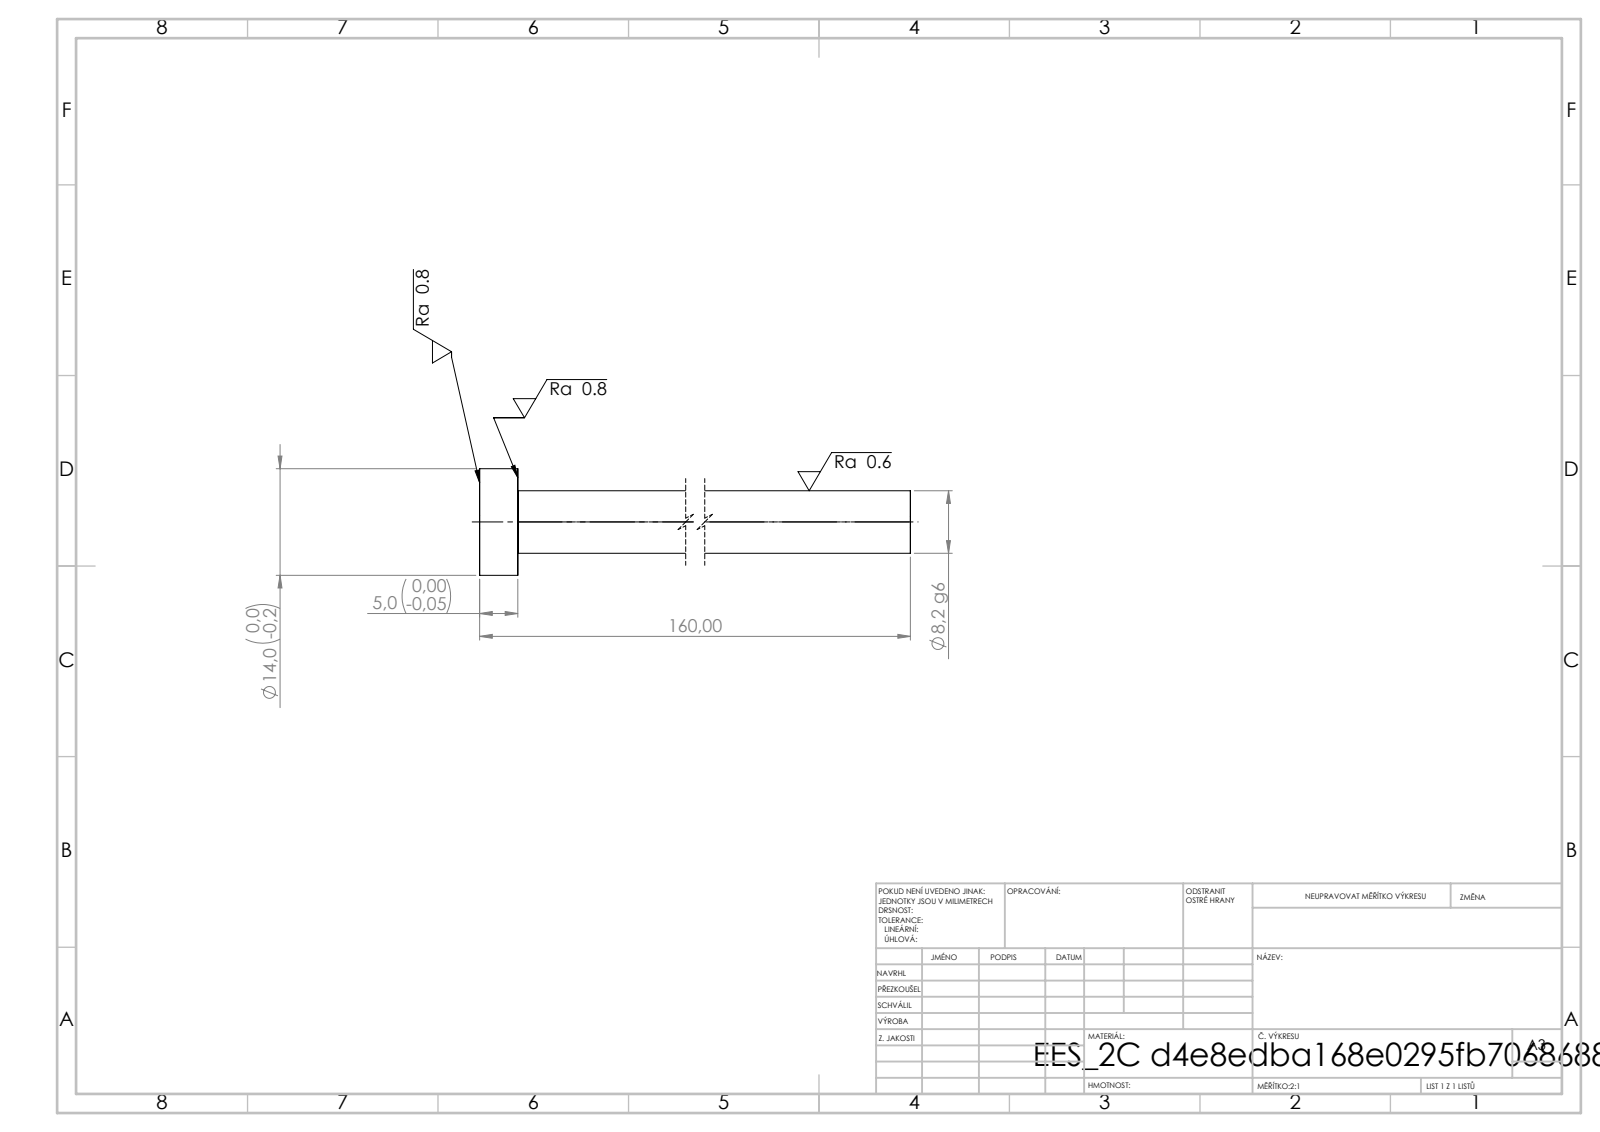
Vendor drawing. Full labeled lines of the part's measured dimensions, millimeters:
STEP written by: SolidWorks 2019 (CONFIG_CONTROL_DESIGN)
Units: millimetres
Bodies: 1 solid, 7 faces (3 planar, 4 cylindrical, 0 other)
Overall size (bounding box): 160 × 14 × 14
Volume: 8 955 mm³ · Surface area: 4 521 mm²
Round bosses / shafts (diameter × count): ⌀14 ×1, ⌀8.2 ×1
Main face-to-face distances: 5, 160, 155
